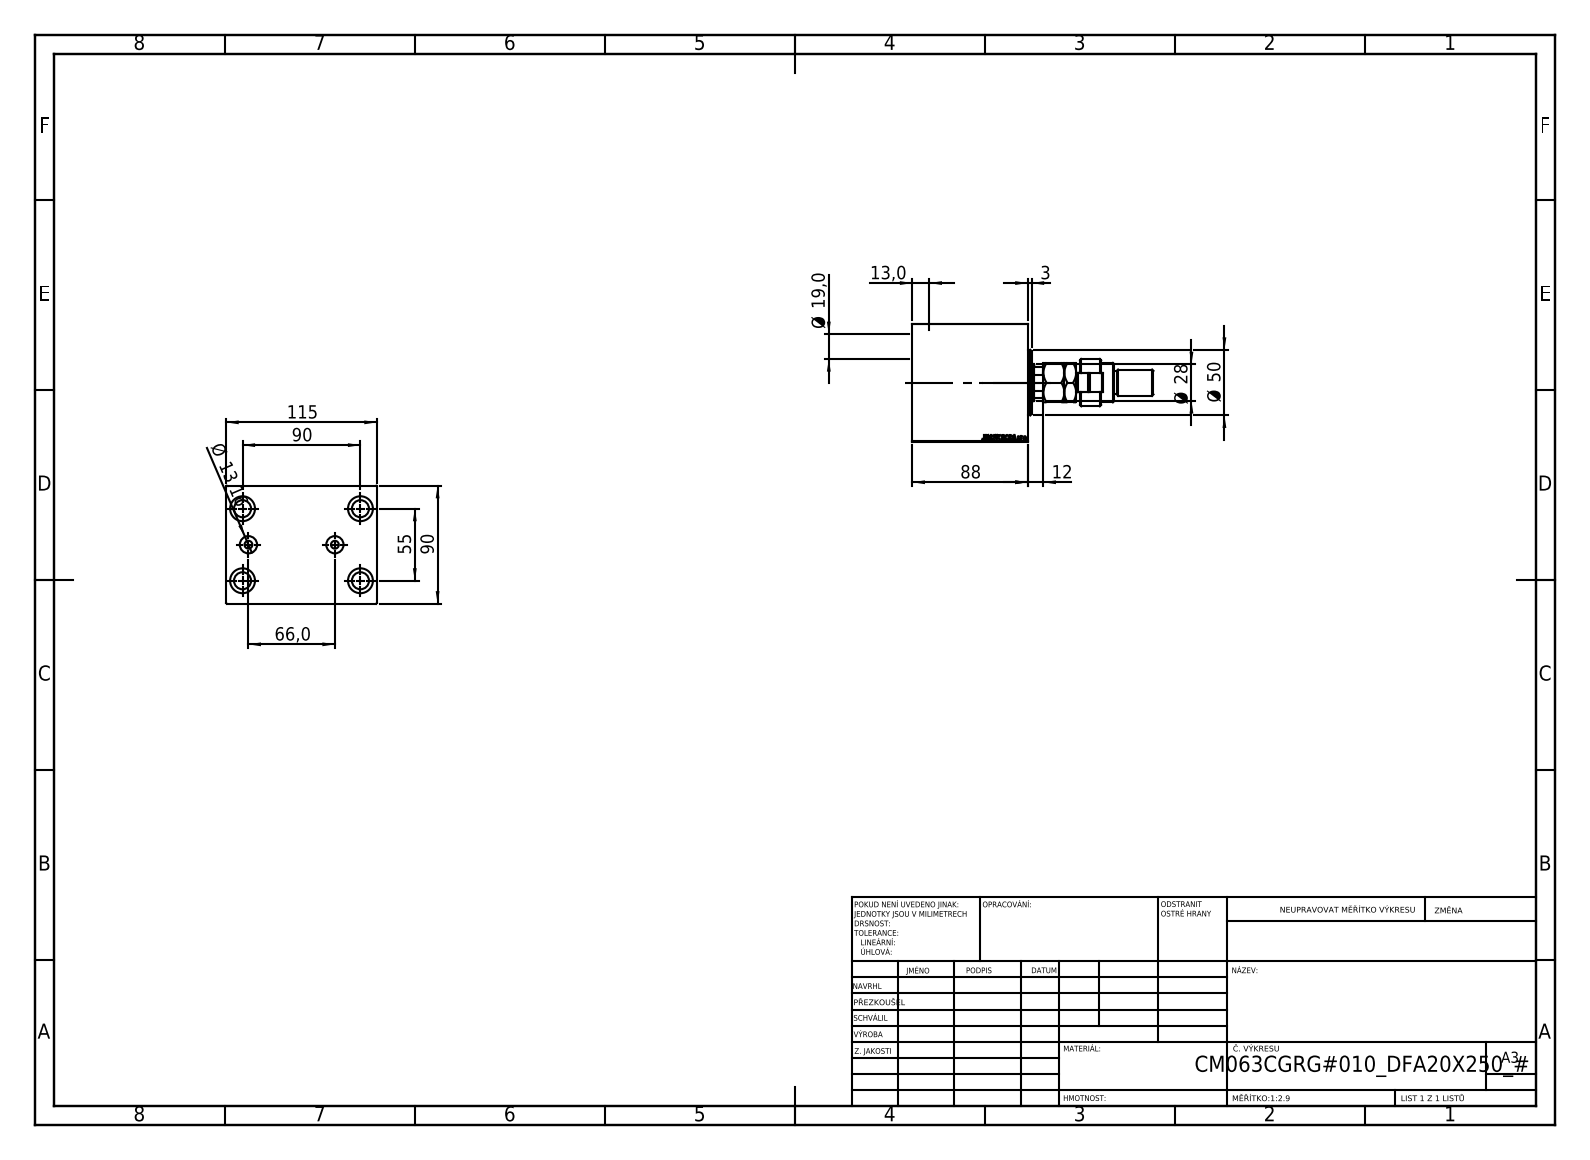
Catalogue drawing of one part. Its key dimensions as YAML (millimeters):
part_name: "FEMALE_PART_FOR_DFA; MFA; V450CM_C_VCP; V450CM_VC_B (+1 more)"
step_written_by: "SolidWorks 2019 (CONFIG_CONTROL_DESIGN)"
units: millimeters
bodies: {solids: 5, faces: 945, planar: 436, cylindrical: 71, other: 438}
overall_size: [184, 115, 90]
volume: 869794
surface_area: 127527
round_holes:
  - {diameter: 13, count: 4}
  - {diameter: 19, count: 4}
  - {diameter: 6, count: 2}
  - {diameter: 13.16, count: 2}
  - {diameter: 18.5, count: 1}
  - {diameter: 28, count: 1}
  - {diameter: 31.5, count: 1}
  - {diameter: 63, count: 1}
  - {diameter: 65, count: 1}
  - {diameter: 72, count: 1}
round_bosses_or_shafts:
  - {diameter: 50, count: 1}
  - {diameter: 36, count: 1}
  - {diameter: 30, count: 1}
  - {diameter: 22, count: 1}
  - {diameter: 20, count: 1}
  - {diameter: 18, count: 1}
  - {diameter: 14, count: 1}
partial_cylinders:
  - {radius: 7.5, count: 1}
  - {radius: 12, count: 1}
  - {radius: 13.5, count: 1}
face_to_face_distances: [90, 115, 88, 37, 51, 10, 21.6, 29.4, 66.4, 56.4]
hole_center_spacings: [52.74, 27.87, 33.71, 55, 75.67, 89.81, 90, 105.48]
